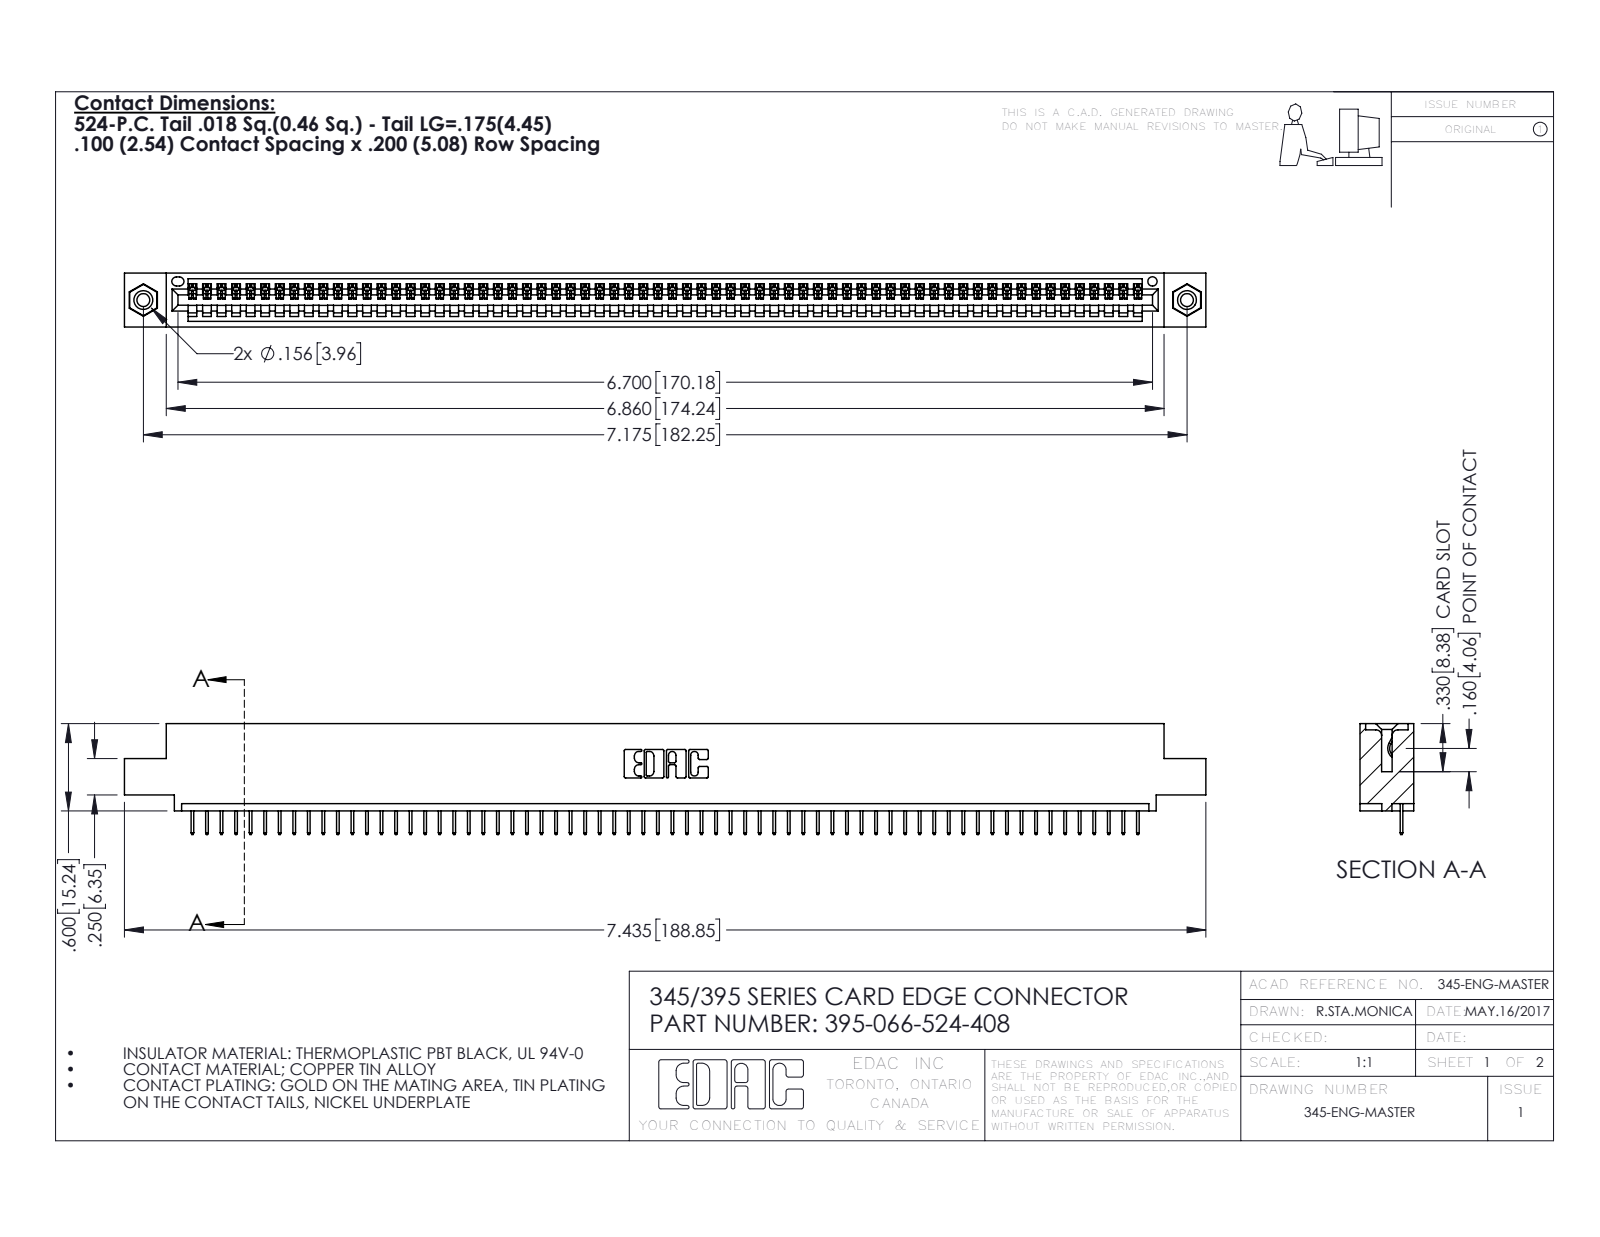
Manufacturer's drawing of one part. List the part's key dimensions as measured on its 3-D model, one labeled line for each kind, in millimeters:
Part name (STEP PRODUCT): 345-250-001_345-250-003-102; 395-066-524-408; 345 Part_0.110 Offset - 0.156 Dia-TI; 345-292-001_345-293-124
STEP written by: SolidWorks 2016 (CONFIG_CONTROL_DESIGN)
Units: millimetres
Bodies: 69 solids, 4282 faces (3152 planar, 1114 cylindrical, 16 other)
Overall size (bounding box): 188.8 × 19.4 × 9.4
Volume: 17 800 mm³ · Surface area: 23 240 mm²
Round holes (diameter × count): ⌀2.3 ×2, ⌀3.2 ×2, ⌀4 ×2, ⌀1.6 ×1
Round bosses / shafts (diameter × count): ⌀3.9 ×2
Partial cylindrical surfaces — rounded edges, fillets, slot ends (radius × count): R0.2 ×132, R0.3 ×22, R0.2 ×6, R0.8 ×6, R0.7 ×3, R0.8 ×2, R1 ×2, R0.4 ×1
Main face-to-face distances: 1.8, 7.6, 9.4, 5.1, 2.5, 6.9, 0.6, 5.7, 1.8, 3.8
Hole centre spacings: 6.9, 176.3, 182.2
